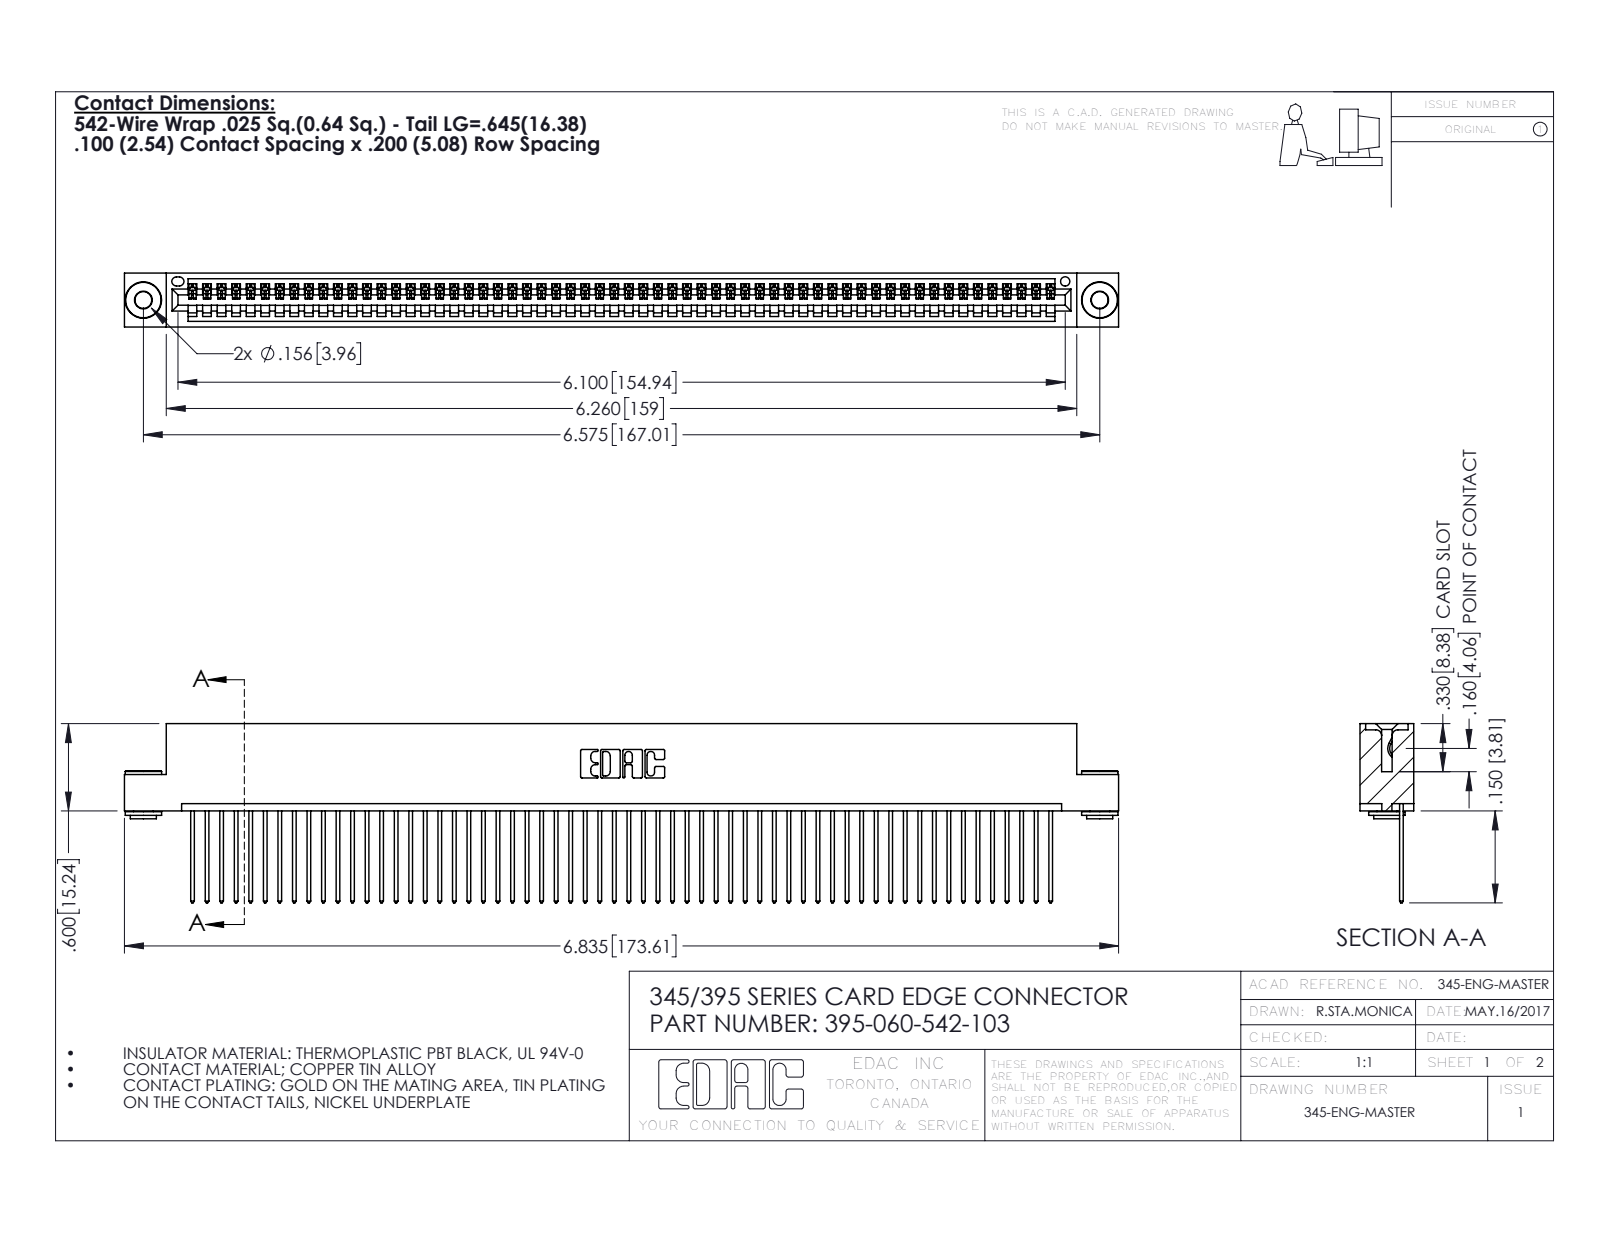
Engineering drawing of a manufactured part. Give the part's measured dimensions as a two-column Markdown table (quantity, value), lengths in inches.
| quantity | value |
| --- | --- |
| part name | 395-060-542-103; 345-250-002_345-250-002-102; 345 Part_Flush Mounting Lugs - 0.156 Dia-TH; 345-292-001_345-293-142 |
| STEP written by | SolidWorks 2016 (CONFIG_CONTROL_DESIGN) |
| units | inches |
| bodies | 63 solids, 3644 faces (2490 planar, 1146 cylindrical, 8 other) |
| overall size | 6.835 × 1.232 × 0.37 |
| volume | 1.025 in³ |
| surface area | 36.6 in² |
| round holes (diameter × count) | 0.116 × 2, 0.156 × 2, 0.064 × 1 |
| round bosses / shafts (diameter × count) | 0.25 × 2, 0.18 × 2, 0.136 × 2 |
| partial cylindrical surfaces (radius × count) | 0.006 × 120, 0.01 × 120, 0.01 × 22, 0.007 × 6, 0.031 × 6, 0.026 × 3, 0.031 × 2, 0.04 × 2 |
| main face-to-face distances | 0.072, 0.298, 0.025, 0.098, 0.272, 0.37, 0.2, 0.225, 0.149, 0.072 |
| hole center spacings | 0.27, 6.339, 6.575 |
